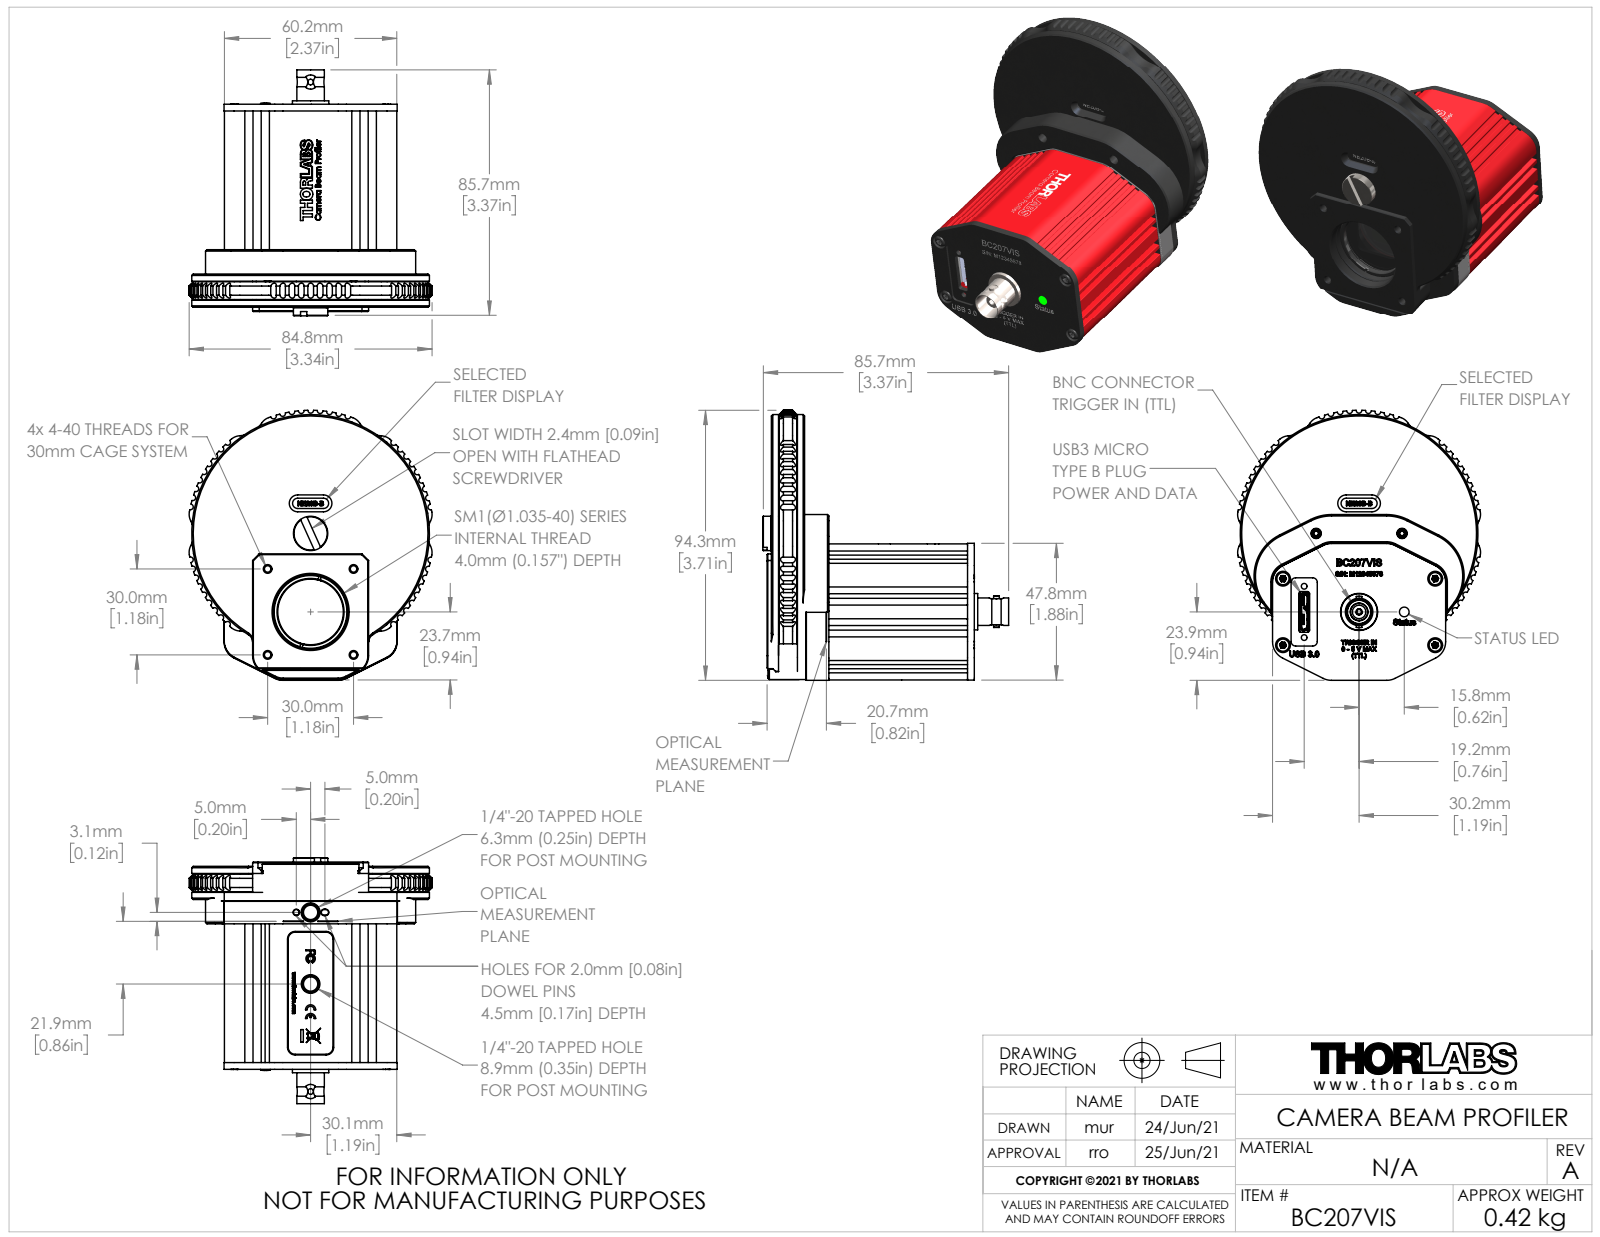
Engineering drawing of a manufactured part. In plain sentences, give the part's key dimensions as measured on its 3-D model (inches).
The part is named "21.08.18_BC207VIS_WEB". Its 3-D file was written by "SolidWorks 2019 (AUTOMOTIVE_DESIGN)". It is 58 solids with 6116 faces: 3322 planar, 1208 cylindrical and 1586 other. Overall it measures 3.711 by 3.38 by 3.341 inches. Its volume is 8.759 cubic inches and its surface area 165.6 square inches. Round holes: 8 of diameter 0.089, 7 of diameter 1.022, 6 of diameter 0.031, 6 of diameter 0.902, 6 of diameter 0.906, 6 of diameter 1.004, 6 of diameter 1.043, 5 of diameter 0.063, 5 of diameter 0.07, 5 of diameter 0.079, 5 of diameter 0.086, 4 of diameter 0.112. Round bosses or shafts: 226 of diameter 0.027, 7 of diameter 0.984, 4 of diameter 1.035, 4 of diameter 0.232, 4 of diameter 0.167, 4 of diameter 0.04, 3 of diameter 1.035, 2 of diameter 0.2. Partial cylindrical surfaces (rounded edges, fillets, slot ends): 79 of radius 0.008, 58 of radius 0.039, 56 of radius 0.004, 48 of radius 0.006, 48 of radius 0.032, 28 of radius 0.02, 28 of radius 0.25, 24 of radius 0.032. The main face-to-face distances are 0.098, 0.358, 0.26, 0.335, 0.252, 0.35, 0.106, 0.378, 0.118, 0.476. The hole center spacings are 0.591, 1.079, 1.181, 2.093, 0.475, 0.581, 0.598, 0.687.
